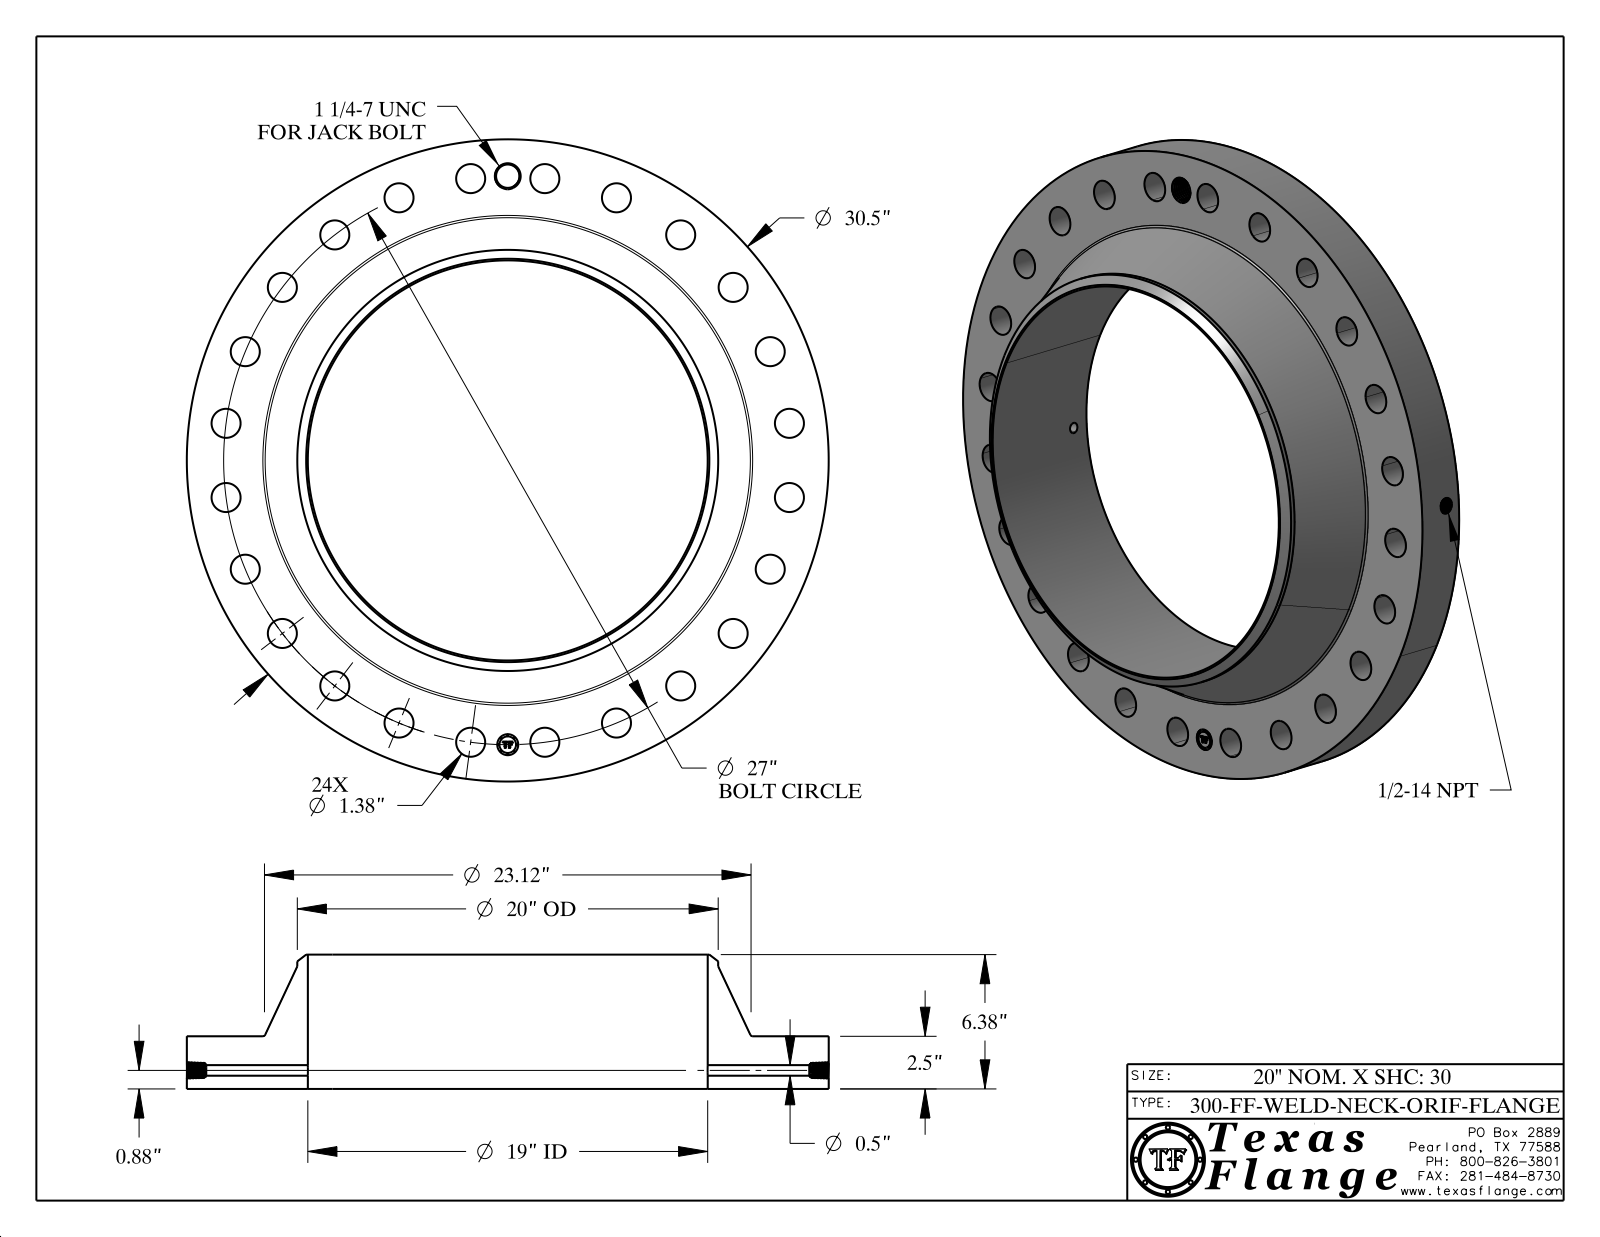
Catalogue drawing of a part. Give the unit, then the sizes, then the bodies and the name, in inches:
Units: inches
Overall size (bounding box): 30.5 × 30.5 × 6.38
Round holes (diameter × count): ⌀1.38 ×24, ⌀0.5 ×1, ⌀0.672 ×1, ⌀1 ×1, ⌀1.109 ×1, ⌀19 ×1
Round bosses / shafts (diameter × count): ⌀0.061 ×8, ⌀30.5 ×1, ⌀20 ×1, ⌀0.788 ×1
Main face-to-face distances: 2.5, 6.38, 3.88, 2.485, 0.015, 3.895, 0.298, 0.293, 0.054, 0.248
Hole centre spacings: 13.5, 23.383, 24.945, 21.42, 3.524, 6.988, 19.092, 26.08
Volume: 1 308 in³ · Surface area: 1 898 in²
Bodies: 1 solid, 815 faces (368 planar, 129 cylindrical, 318 other)
Part name (STEP PRODUCT): 300-FF-WELD-NECK
STEP written by: CATIA V5 STEP AP214 (AUTOMOTIVE_DESIGN)
